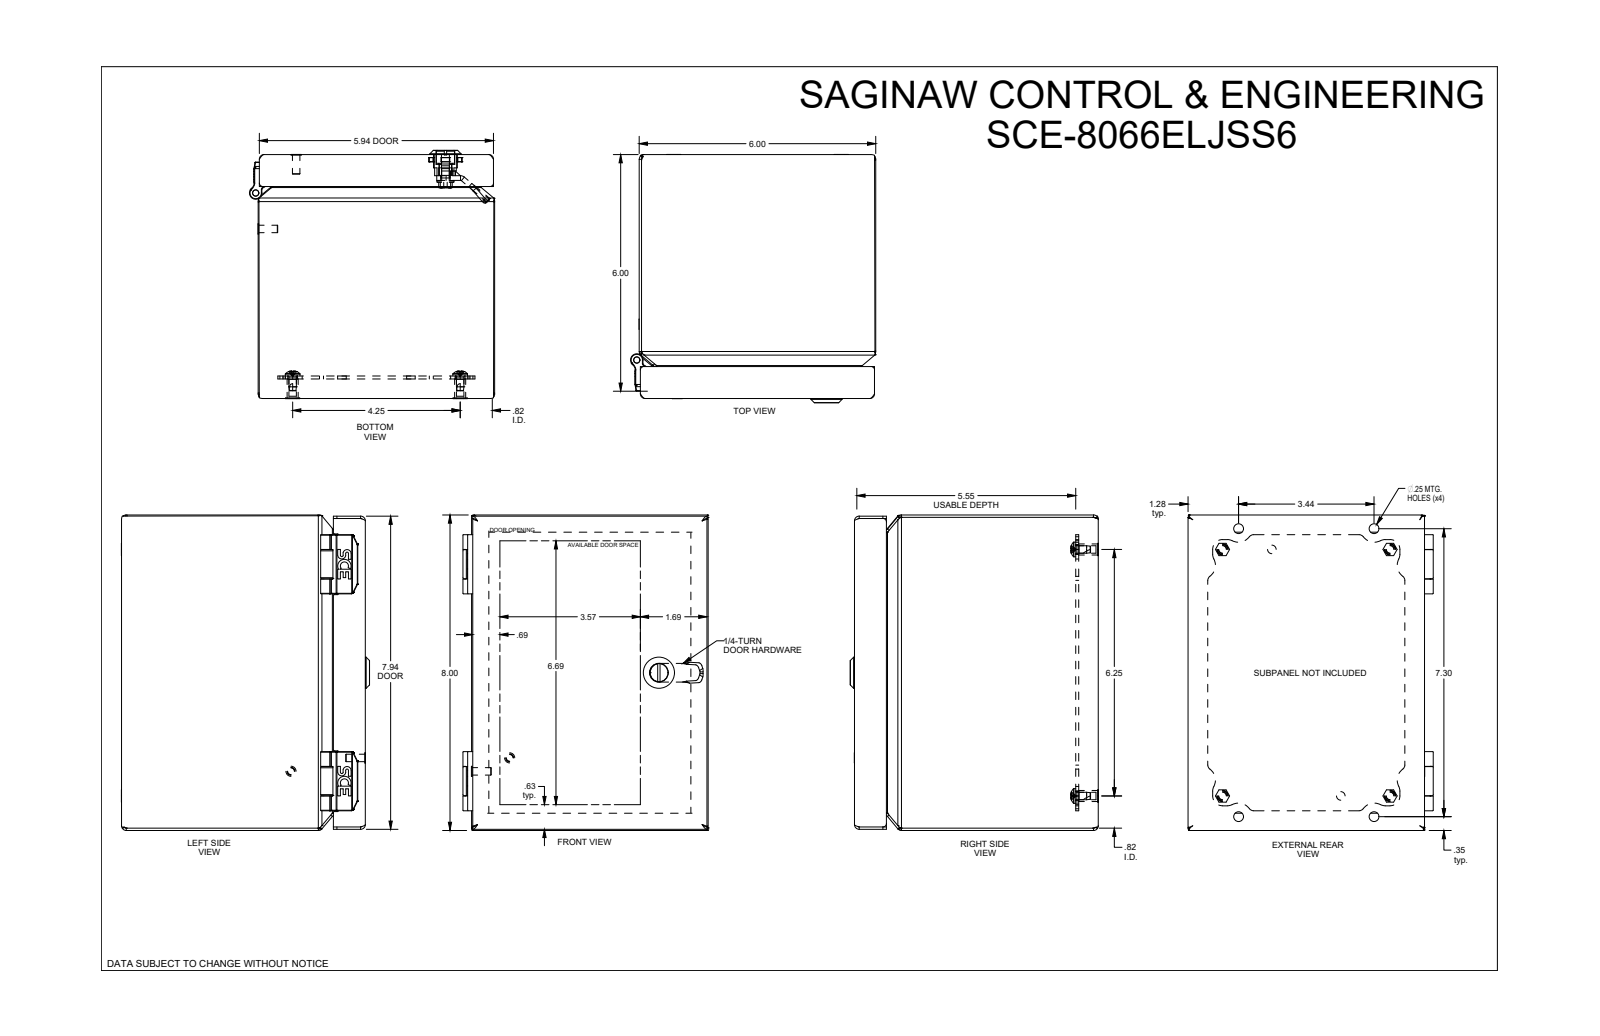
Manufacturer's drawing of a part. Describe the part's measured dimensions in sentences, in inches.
The part is named "SCE-8066ELJSS6". Its 3-D file was written by "SolidWorks 2019 (CONFIG_CONTROL_DESIGN)". It is 0 solids with 2717 faces: 863 planar, 790 cylindrical and 1064 other. Overall it measures 8 by 6.296 by 6.22 inches. Round holes: 8 of diameter 0.25, 4 of diameter 0.19, 4 of diameter 0.284, 4 of diameter 0.479, 2 of diameter 0.02, 2 of diameter 0.1, 2 of diameter 0.174, 2 of diameter 0.196, 2 of diameter 0.218, 2 of diameter 0.266, 1 of diameter 0.158, 1 of diameter 0.2. Round bosses or shafts: 6 of diameter 0.188, 4 of diameter 0.373, 4 of diameter 0.28, 4 of diameter 0.17, 4 of diameter 0.16, 4 of diameter 0.135, 4 of diameter 0.108, 2 of diameter 0.26. Partial cylindrical surfaces (rounded edges, fillets, slot ends): 132 of radius 0.106, 131 of radius 0.005, 32 of radius 0.008, 26 of radius 0.008, 24 of radius 0.025, 24 of radius 0.03, 23 of radius 0.12, 22 of radius 0.06. The main face-to-face distances are 0.06, 5.94, 0.06, 7.94, 6.124, 6.065, 6.185, 6.125, 6, 5.88. The hole center spacings are 0.663, 3.88, 6.787, 7.789, 0.994, 1.25, 2.646, 3.
